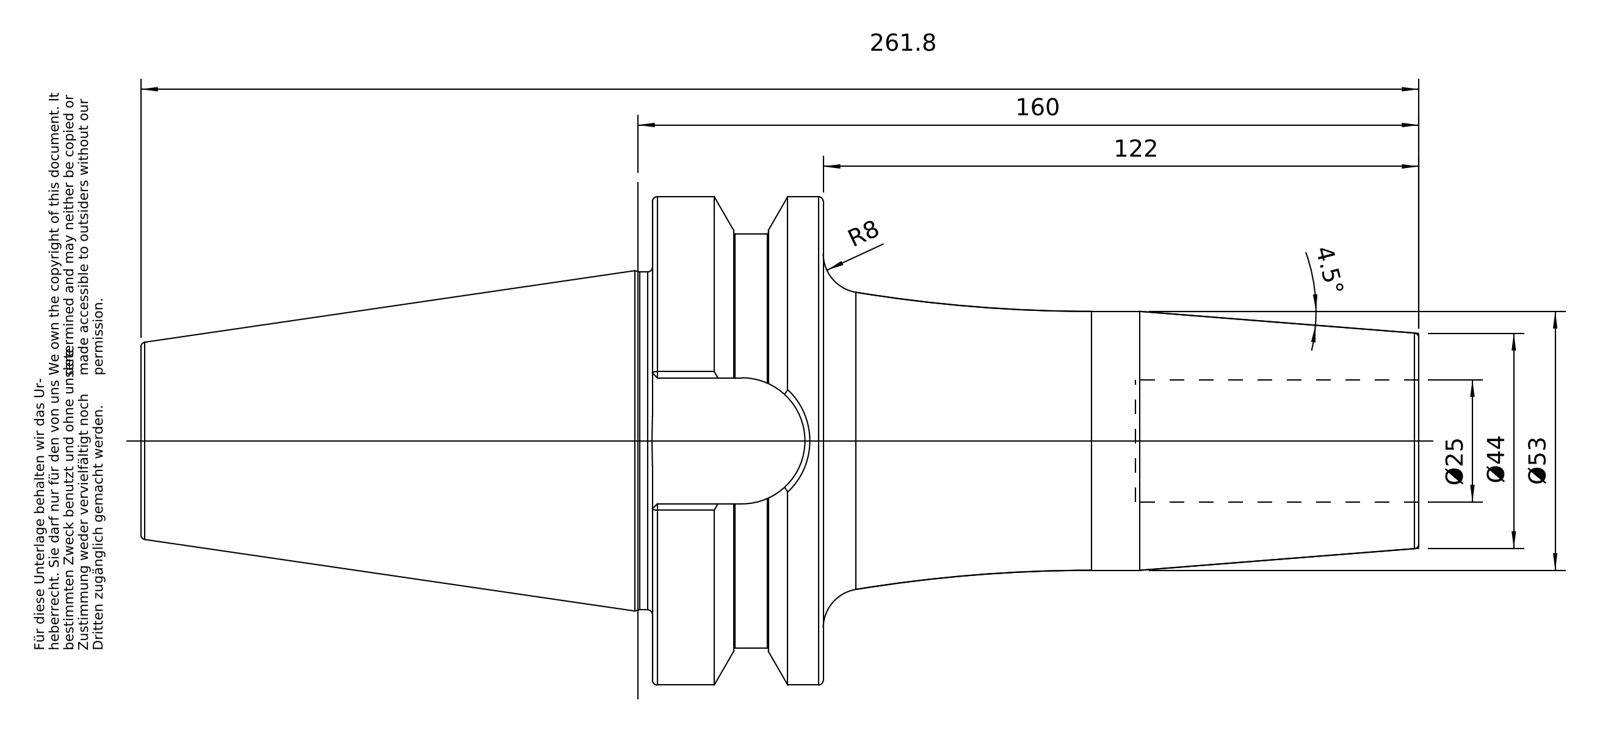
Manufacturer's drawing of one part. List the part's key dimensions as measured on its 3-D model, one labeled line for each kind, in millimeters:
Part name (STEP PRODUCT): 50-642-25
STEP written by: PRO/ENGINEER BY PARAMETRIC TECHNOLOGY CORPORATION, 2010430 (CONFIG_CONTROL_DESIGN)
Units: millimetres
Bodies: 1 solid, 98 faces (26 planar, 22 cylindrical, 50 other)
Overall size (bounding box): 261.8 × 99.97 × 99.97
Volume: 706 738 mm³ · Surface area: 74 487 mm²
Round holes (diameter × count): ⌀20.75 ×1, ⌀25 ×1, ⌀25.02 ×1, ⌀25.7 ×1
Round bosses / shafts (diameter × count): ⌀99.97 ×1, ⌀84.75 ×1, ⌀69.15 ×1, ⌀53 ×1, ⌀24.01 ×1
Partial cylindrical surfaces — rounded edges, fillets, slot ends (radius × count): R12.9 ×1
Main face-to-face distances: 35, 157, 122, 70.4, 104.8, 139.8, 261.8, 203.8, 99, 64
